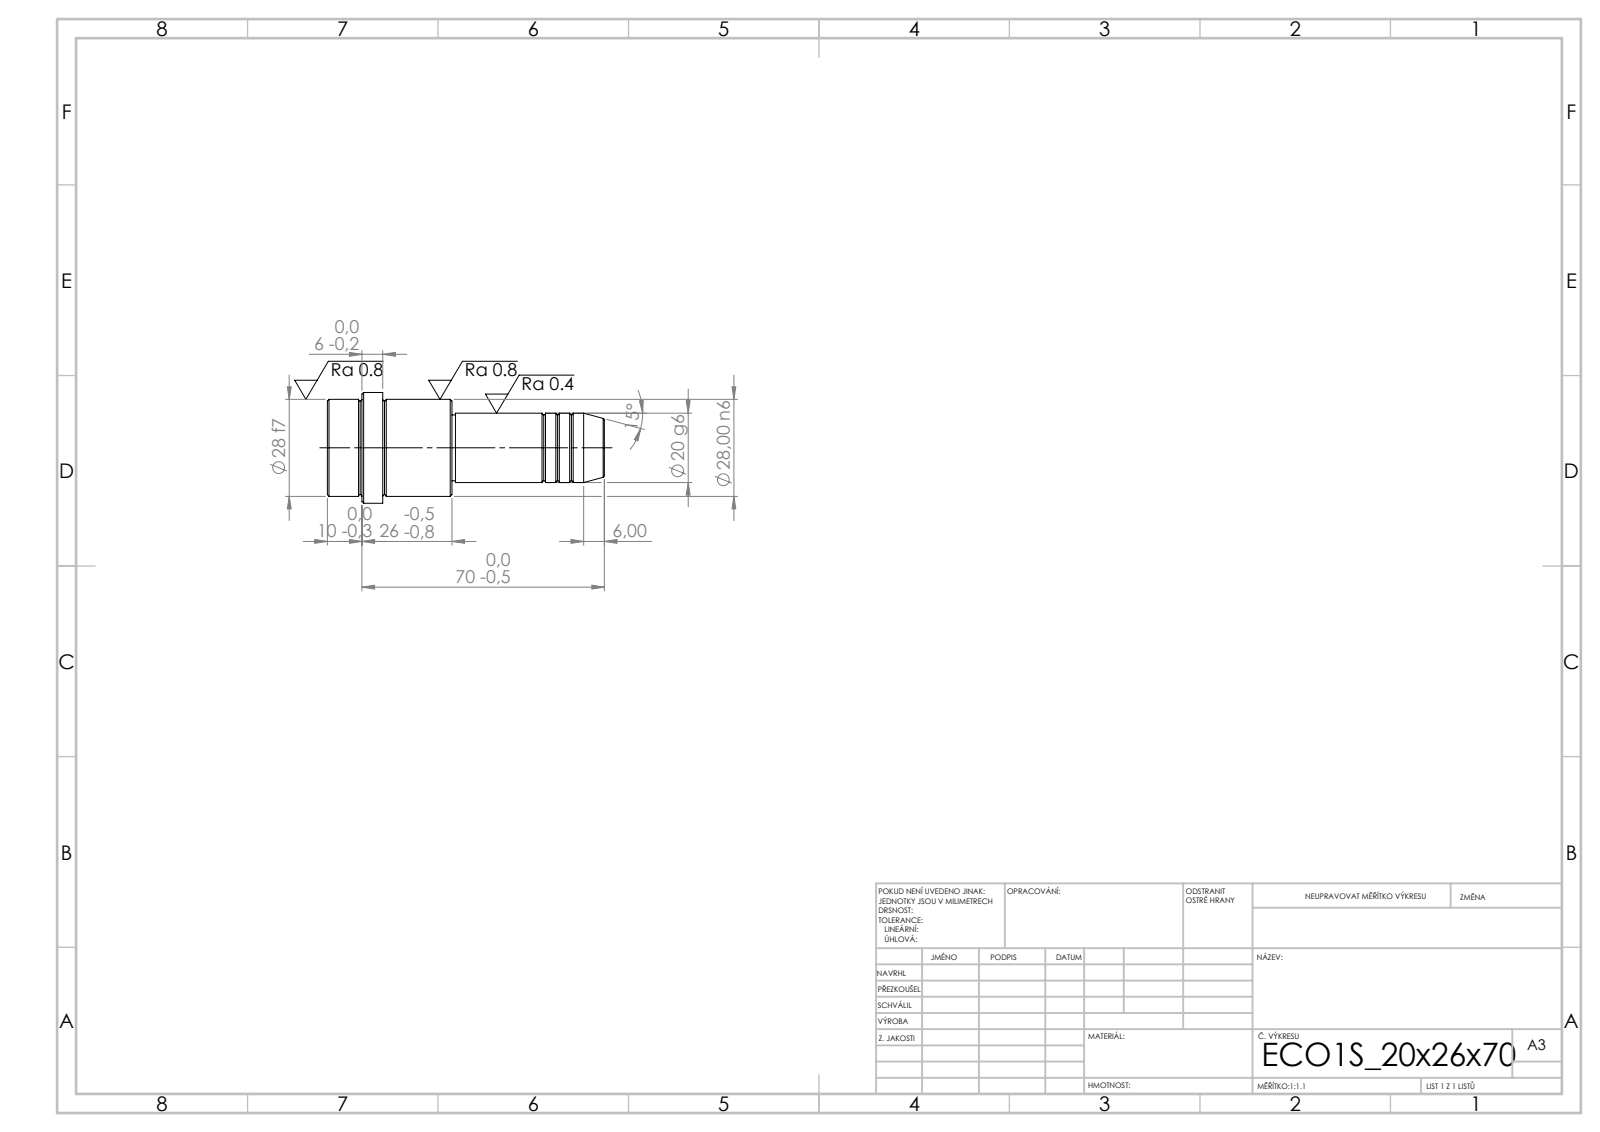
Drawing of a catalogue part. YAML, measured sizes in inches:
step_written_by: "SolidWorks 2019 (CONFIG_CONTROL_DESIGN)"
units: inches
bodies: {solids: 1, faces: 52, planar: 6, cylindrical: 16, other: 30}
overall_size: [3.15, 1.26, 1.26]
volume: 2.235
surface_area: 11.88
round_bosses_or_shafts:
  - {diameter: 1.26, count: 1}
  - {diameter: 1.102, count: 1}
  - {diameter: 0.787, count: 1}
  - {diameter: 0.748, count: 1}
face_to_face_distances: [1.417, 1.732, 3.15, 2.52, 0.787, 0.63, 2.756, 1.024, 0.236, 0.394]
